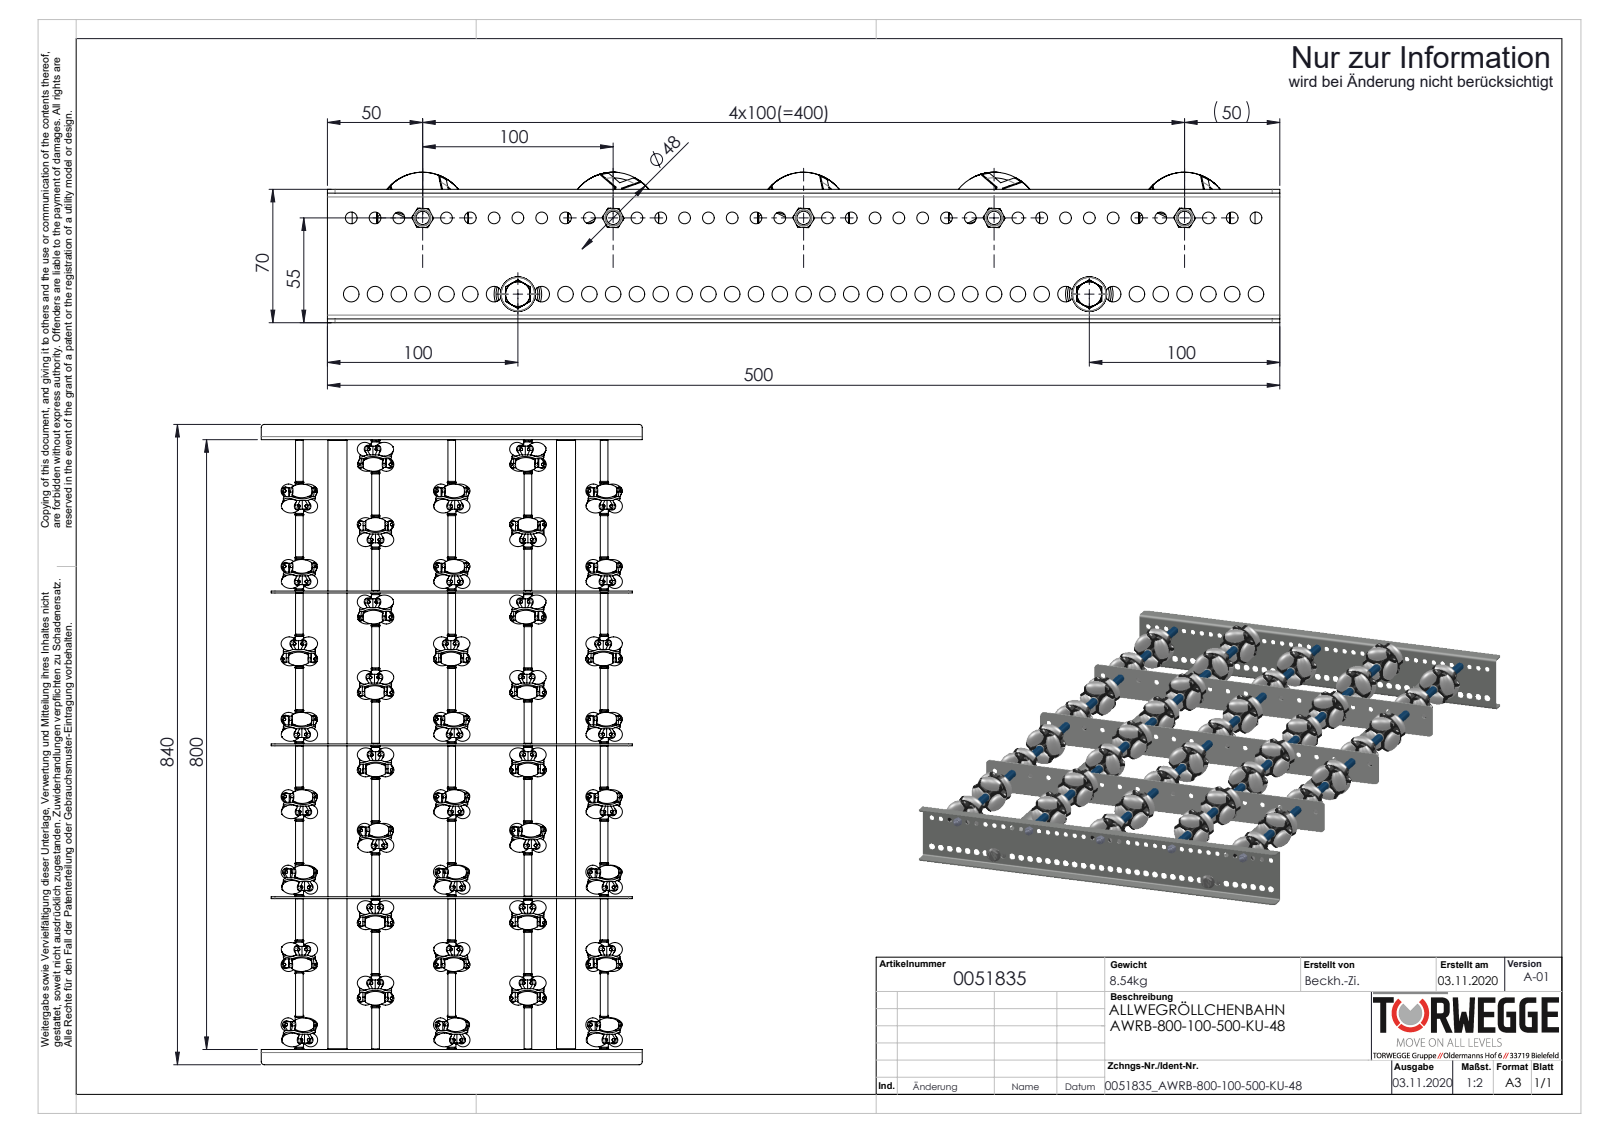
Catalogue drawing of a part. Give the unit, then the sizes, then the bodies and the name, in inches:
Units: inches
Overall size (bounding box): 33.071 × 19.685 × 3.11
Round holes (diameter × count): ⌀0.146 ×240, ⌀0.165 ×240, ⌀0.244 ×39, ⌀0.323 ×39, ⌀0.256 ×19, ⌀0.194 ×5, ⌀0.331 ×5, ⌀0.268 ×2, ⌀0.827 ×2
Round bosses / shafts (diameter × count): ⌀0.157 ×240, ⌀0.146 ×200, ⌀0.315 ×7, ⌀1.854 ×5, ⌀1.654 ×5, ⌀0.433 ×5, ⌀0.394 ×5, ⌀0.276 ×5
Partial cylindrical surfaces — rounded edges, fillets, slot ends (radius × count): R0.157 ×8, R0.079 ×4, R0.197 ×4
Main face-to-face distances: 0.079, 7.894, 0.098, 31.575, 15.787, 0.581, 7.992, 7.795, 0.118, 2.677
Hole centre spacings: 1.419, 1.42, 3.898, 1.42, 4.831, 1.419, 3.327, 0.492
Volume: 153.2 in³ · Surface area: 2 759 in²
Bodies: 670 solids, 11946 faces (4148 planar, 4704 cylindrical, 3094 other)
Part name (STEP PRODUCT): AWR48_Stift; 0027528_BUCHSE-HOHLNIETE ZU AWR48; 0019719_Gewindestange-M6_L=820; S100994_Sperrzahnschraube_M08x16-8.8-A2K (+8 more)
STEP written by: SolidWorks 2020 (AUTOMOTIVE_DESIGN)
